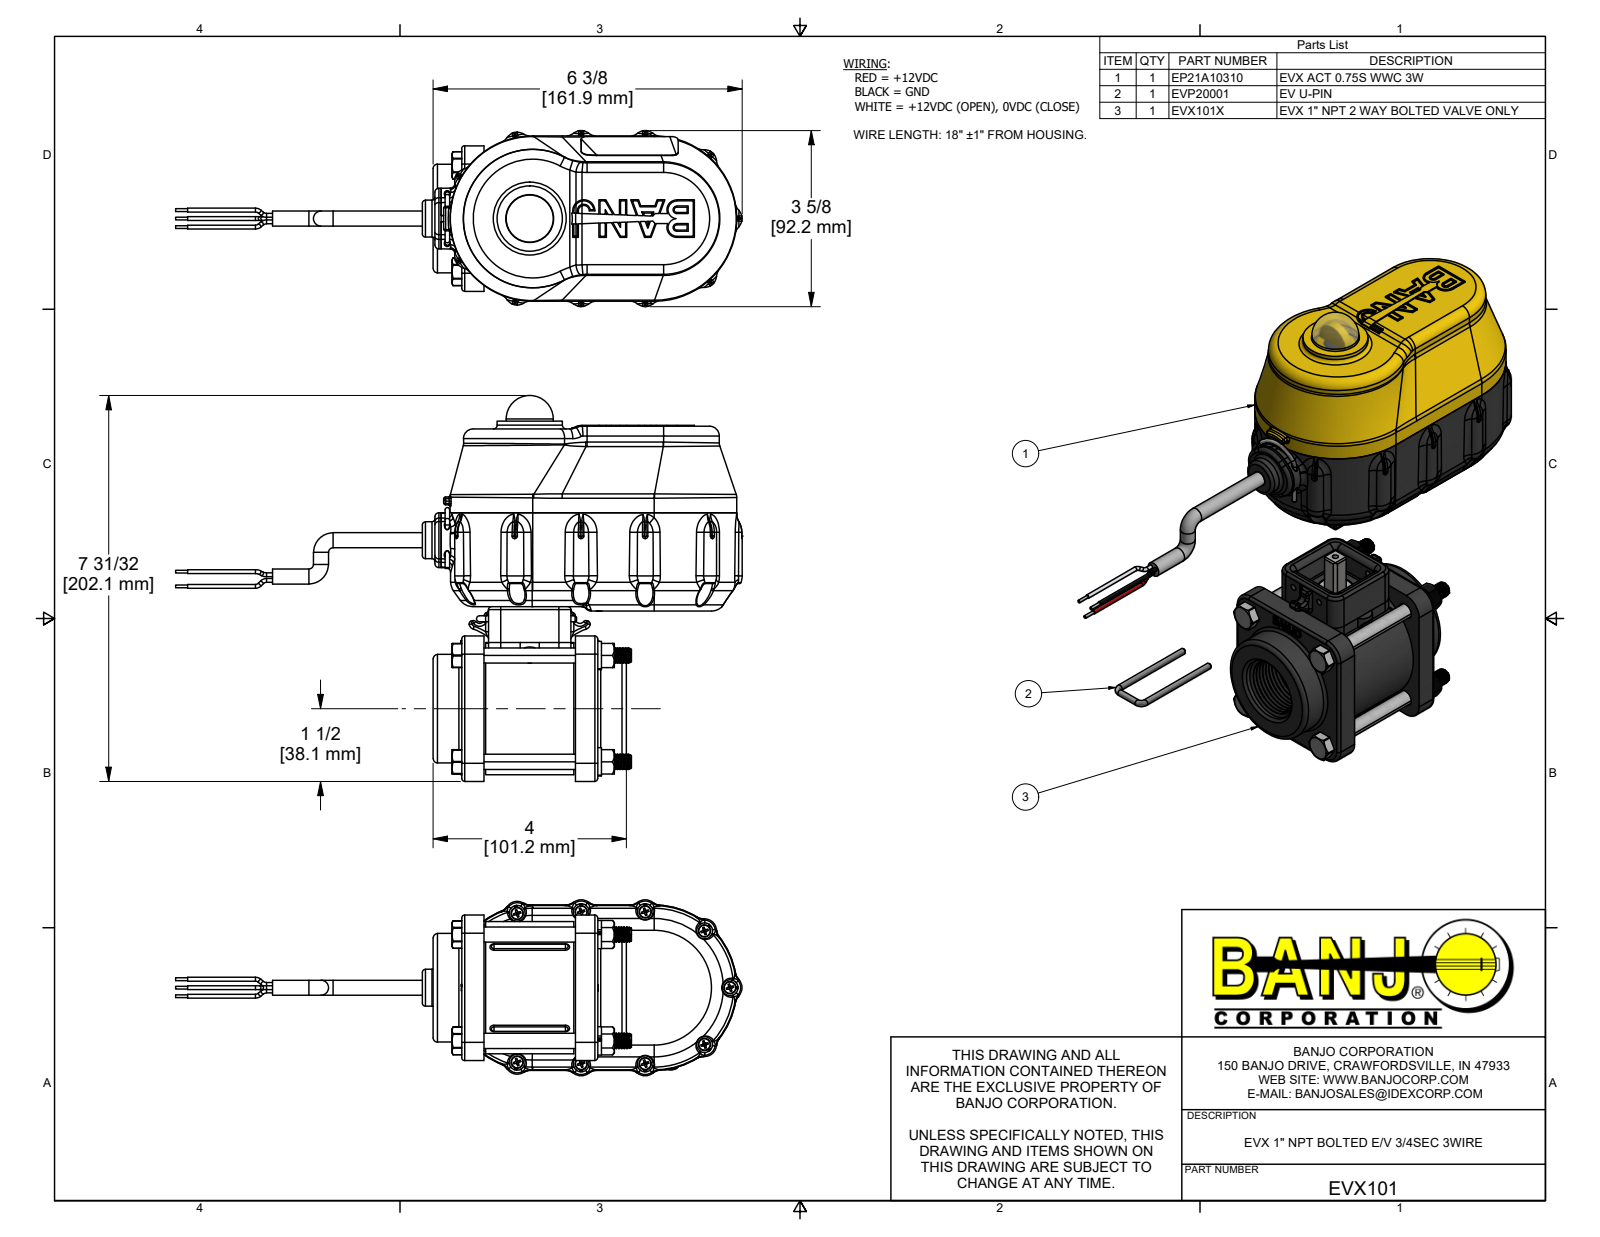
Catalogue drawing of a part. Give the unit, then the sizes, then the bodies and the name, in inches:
Units: inches
Overall size (bounding box): 38.771 × 7.957 × 3.63
Round holes (diameter × count): ⌀0.095 ×11, ⌀0.15 ×11, ⌀0.08 ×7, ⌀0.107 ×4, ⌀0.126 ×4, ⌀0.135 ×4, ⌀0.136 ×4, ⌀0.148 ×4, ⌀0.15 ×4, ⌀0.17 ×4, ⌀0.252 ×4, ⌀0.322 ×4
Round bosses / shafts (diameter × count): ⌀0.268 ×60, ⌀0.25 ×17, ⌀0.08 ×15, ⌀0.14 ×11, ⌀0.108 ×11, ⌀0.085 ×11, ⌀0.058 ×6, ⌀0.313 ×5
Partial cylindrical surfaces — rounded edges, fillets, slot ends (radius × count): R0.013 ×180, R0.04 ×145, R0.01 ×84, R0.02 ×72, R0.06 ×58, R0.005 ×53, R0.03 ×38, R0.08 ×28
Main face-to-face distances: 0.1, 2.565, 0.211, 0.06, 0.151, 0.46, 2.345, 0.055, 0.125, 1.896
Hole centre spacings: 1.046, 1.55, 1.662, 1.891, 2.192, 2.656, 2.69, 2.715
Volume: 50.28 in³ · Surface area: 750.6 in²
Bodies: 96 solids, 11555 faces (2932 planar, 3465 cylindrical, 5158 other)
Part name (STEP PRODUCT): EVX101; EVX101X; MEVX10254A; MEVX10254AX (+8 more)
STEP written by: Autodesk Inventor 2019 (AUTOMOTIVE_DESIGN)
